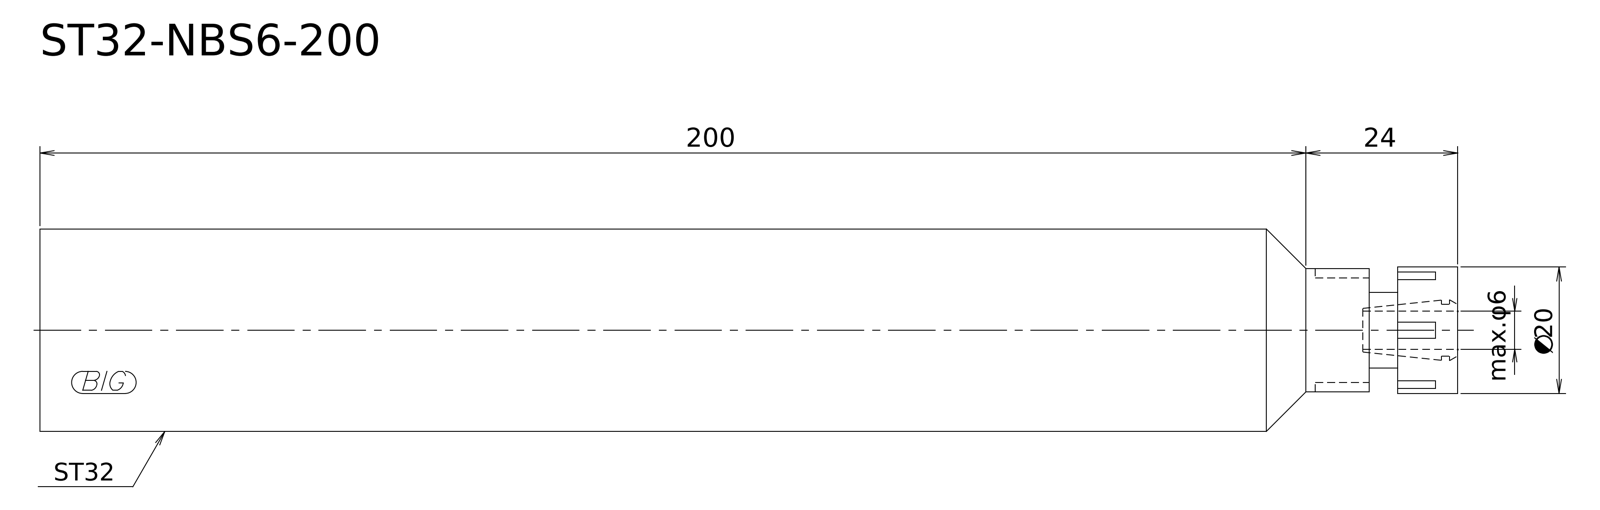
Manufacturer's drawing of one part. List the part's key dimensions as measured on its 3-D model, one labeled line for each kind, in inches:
STEP written by: Kubotek KeyCreator V8.5.1 (14335) (CONFIG_CONTROL_DESIGN)
Units: inches
Bodies: 1 solid, 9 faces (4 planar, 4 cylindrical, 1 other)
Overall size (bounding box): 8.819 × 1.26 × 1.26
Volume: 10.11 in³ · Surface area: 35.77 in²
Round bosses / shafts (diameter × count): ⌀1.26 ×1, ⌀0.787 ×1, ⌀0.768 ×1, ⌀0.472 ×1
Main face-to-face distances: 8.819, 0.374, 8.445, 0.551, 0.177, 8.268
